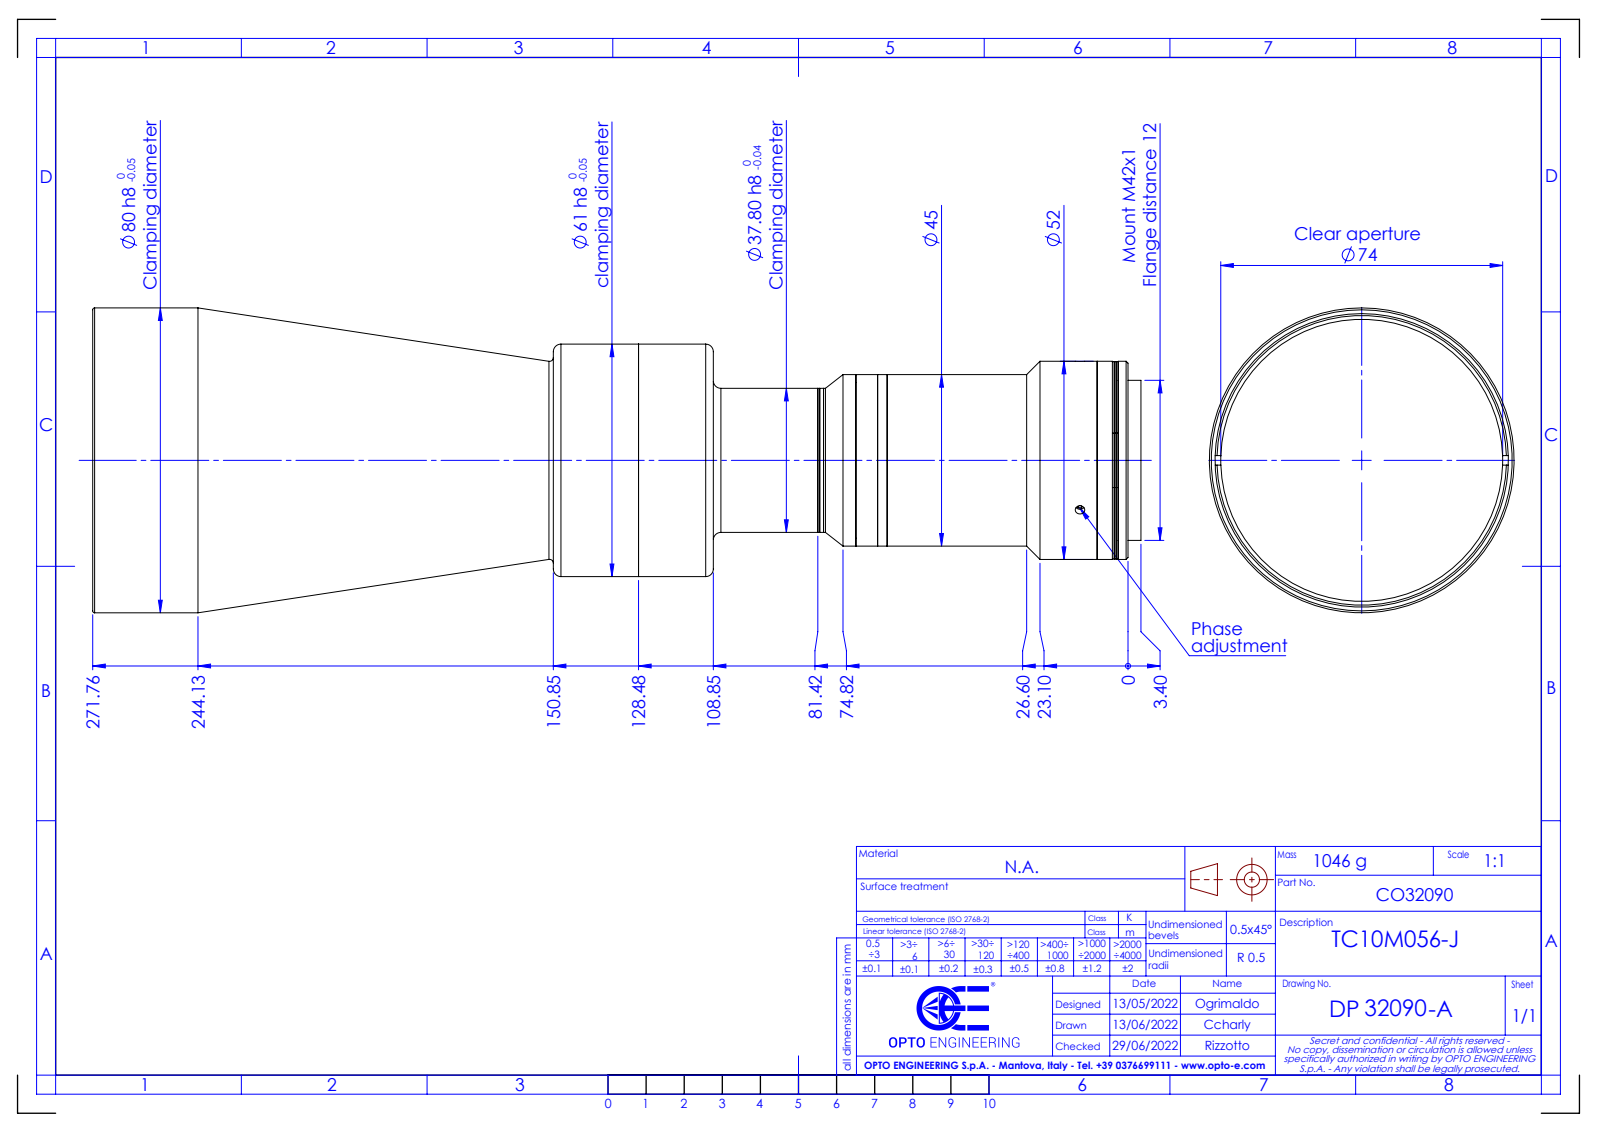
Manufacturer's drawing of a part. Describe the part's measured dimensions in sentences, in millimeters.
The part is named "DP32090-A_TC10M056-J". Its 3-D file was written by "SolidWorks 2021 (CONFIG_CONTROL_DESIGN)". It is 0 solids with 109 faces: 27 planar, 54 cylindrical and 28 other. Overall it measures 275.16 by 80 by 80 millimeters. Round holes: 3 of diameter 2.5, 1 of diameter 38, 1 of diameter 41, 1 of diameter 53, 1 of diameter 74, 1 of diameter 77. Round bosses or shafts: 1 of diameter 80, 1 of diameter 61, 1 of diameter 52, 1 of diameter 51.8, 1 of diameter 45, 1 of diameter 42, 1 of diameter 37.8. The main face-to-face distances are 106.3, 104.76, 1.54, 108.86, 4.1, 2.56, 19.62, 124.38, 125.92, 128.48.
